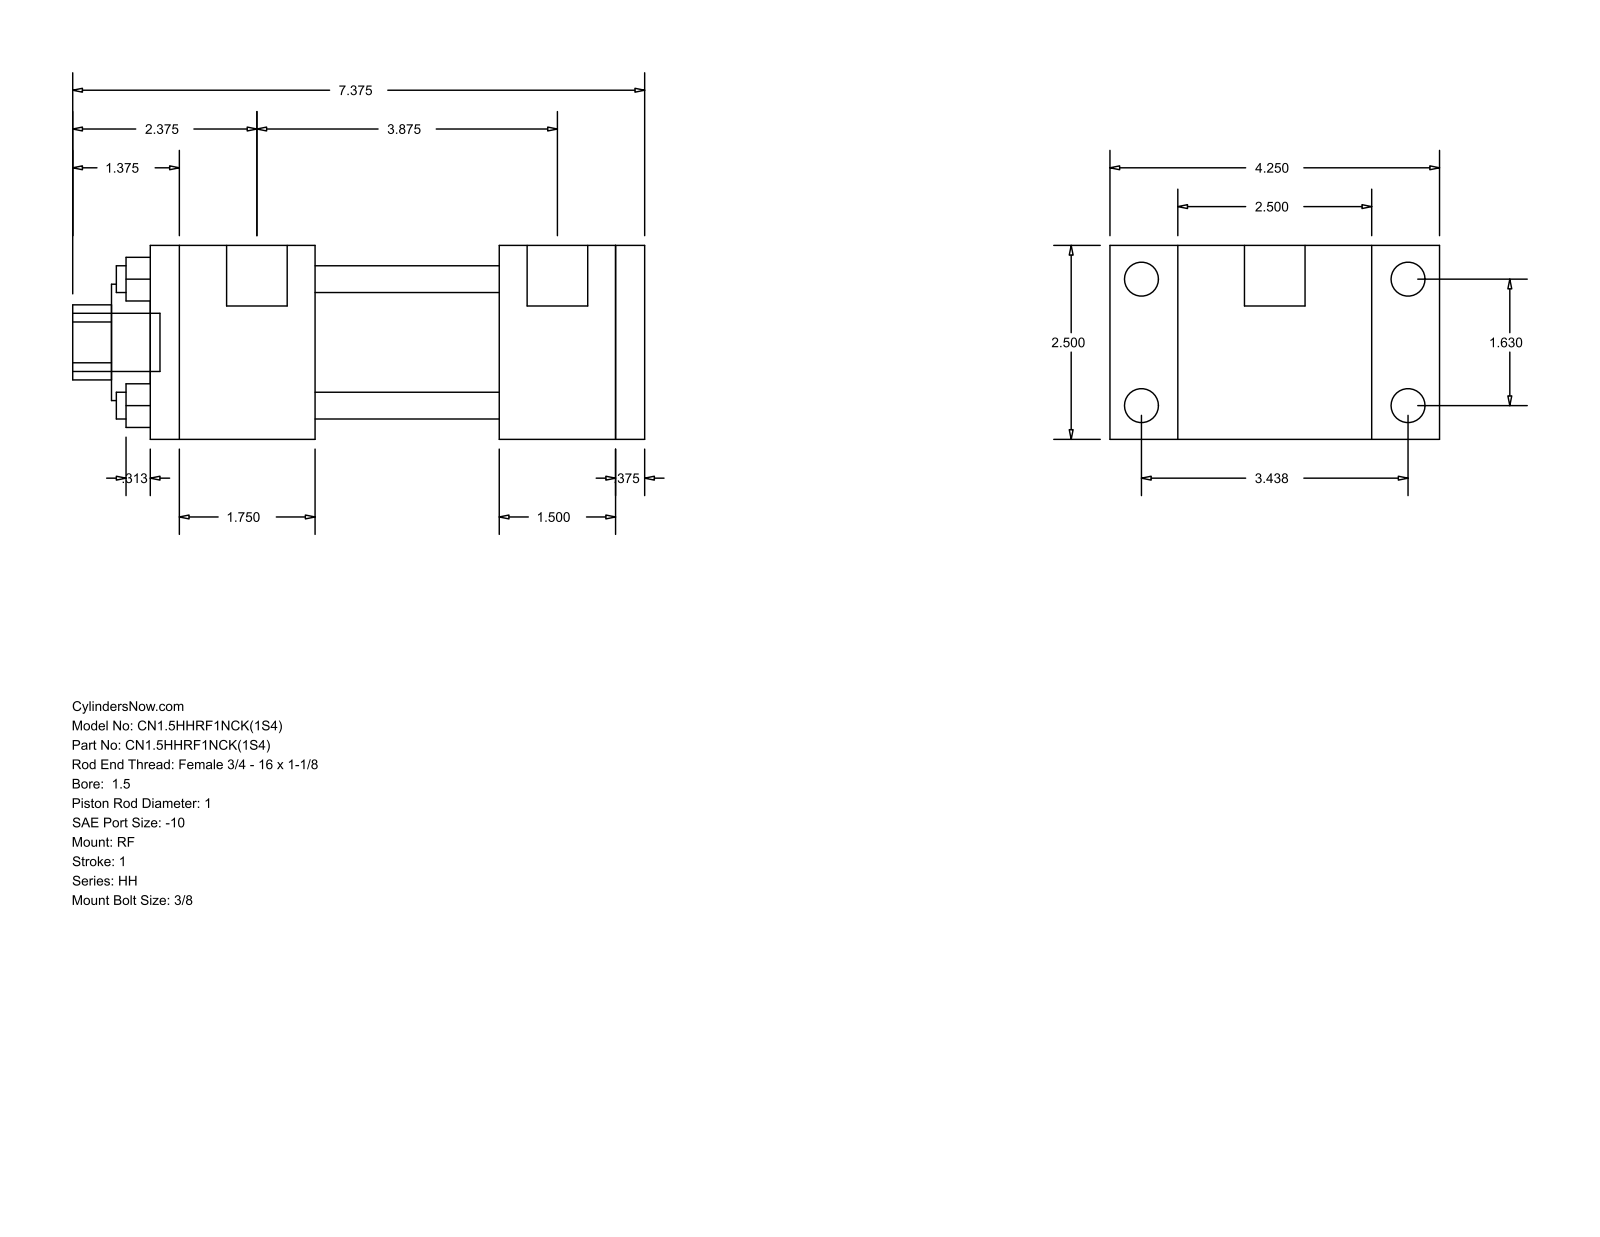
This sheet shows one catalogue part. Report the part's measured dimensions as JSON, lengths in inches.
{"part_name": "HH_RF__0150_1", "step_written_by": "GSSL Pune (CONFIG_CONTROL_DESIGN)", "units": "inches", "bodies": {"solids": 0, "faces": 92, "planar": 64, "cylindrical": 28, "other": 0}, "overall_size": [7.375, 4.25, 2.5], "round_holes": [[0.345, 4], [1, 1], [1.5, 1], [1.75, 1]], "round_bosses_or_shafts": [[0.438, 4], [0.219, 4], [0.781, 2], [0.75, 1]], "partial_cylinders_radius": [[0.484, 1]], "face_to_face_distances": [2.5, 0.375, 2.375, 3.875, 4.25, 1.5, 1.875, 2.125, 4.5, 6], "hole_center_spacings": [1.152, 1.63, 2.305]}
